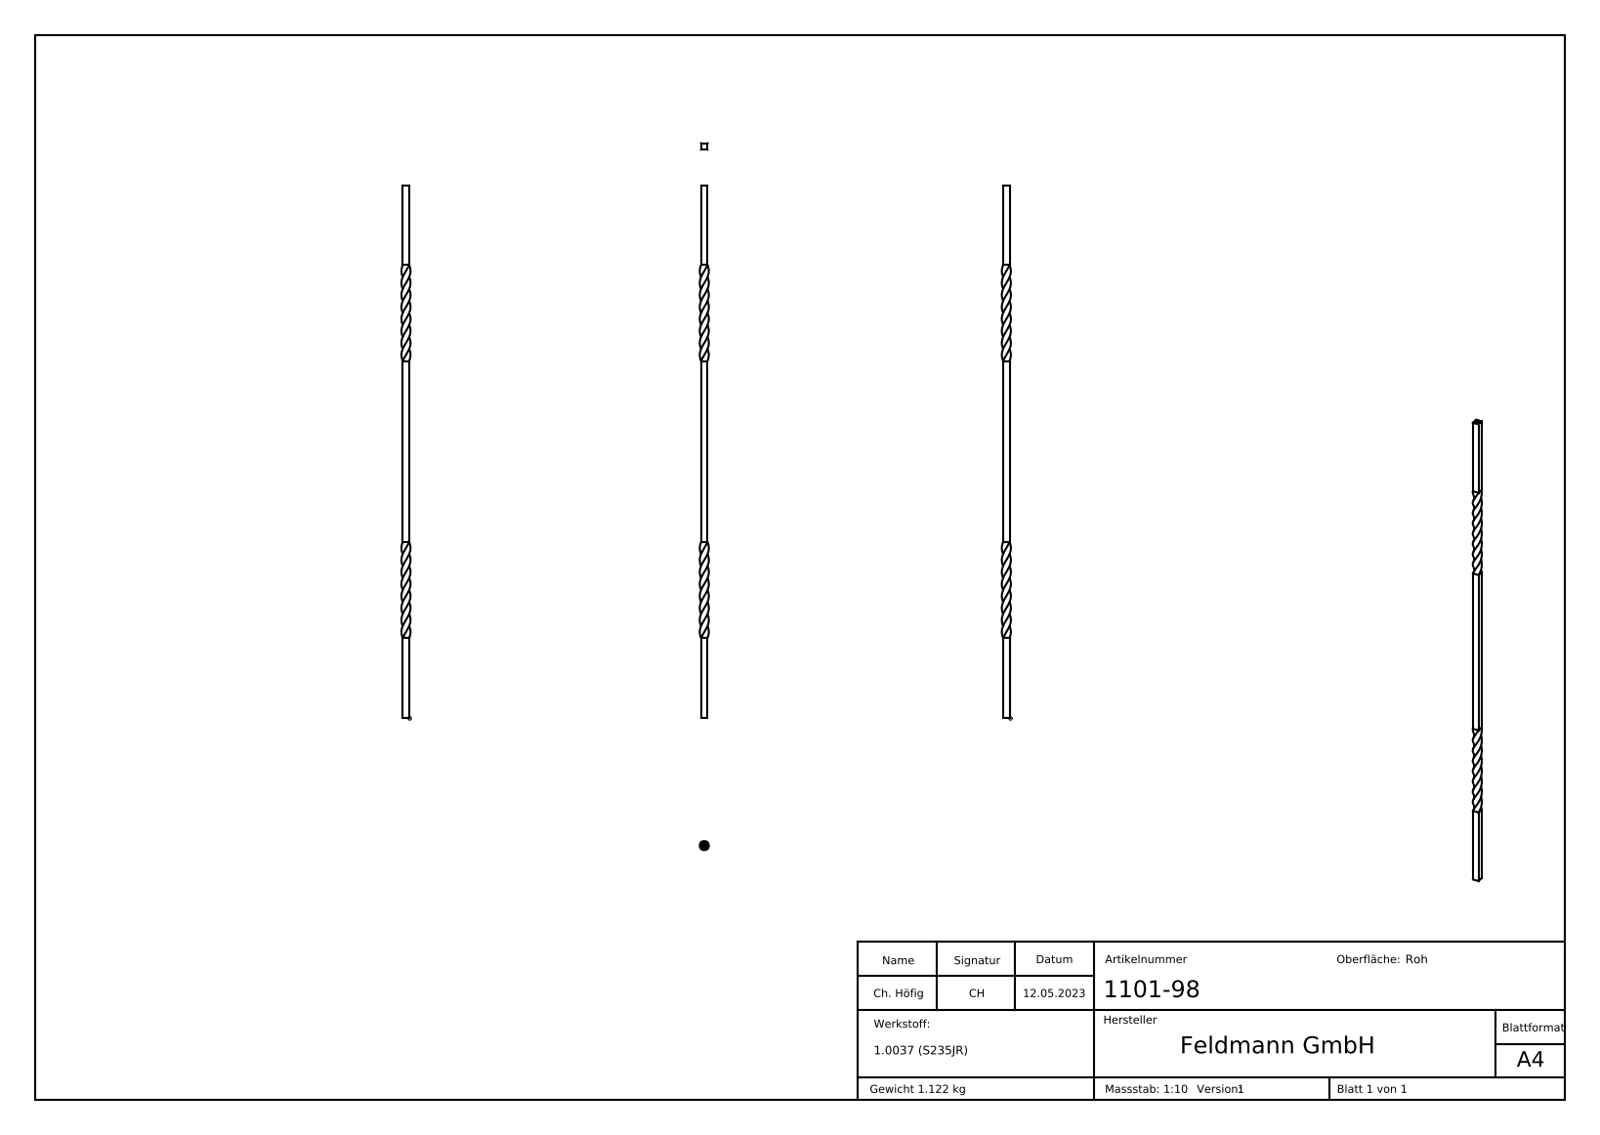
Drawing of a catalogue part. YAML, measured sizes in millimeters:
part_name: "1101-98"
step_written_by: "SolidWorks 2018 (CONFIG_CONTROL_DESIGN)"
units: millimeters
bodies: {solids: 1, faces: 249, planar: 138, cylindrical: 0, other: 111}
overall_size: [1000, 17.03, 17.03]
volume: 143898
surface_area: 48774
face_to_face_distances: [12, 1000, 999.9, 1.14, 2.45, 2.01, 0.63, 1.84, 0.68, 0.75]
